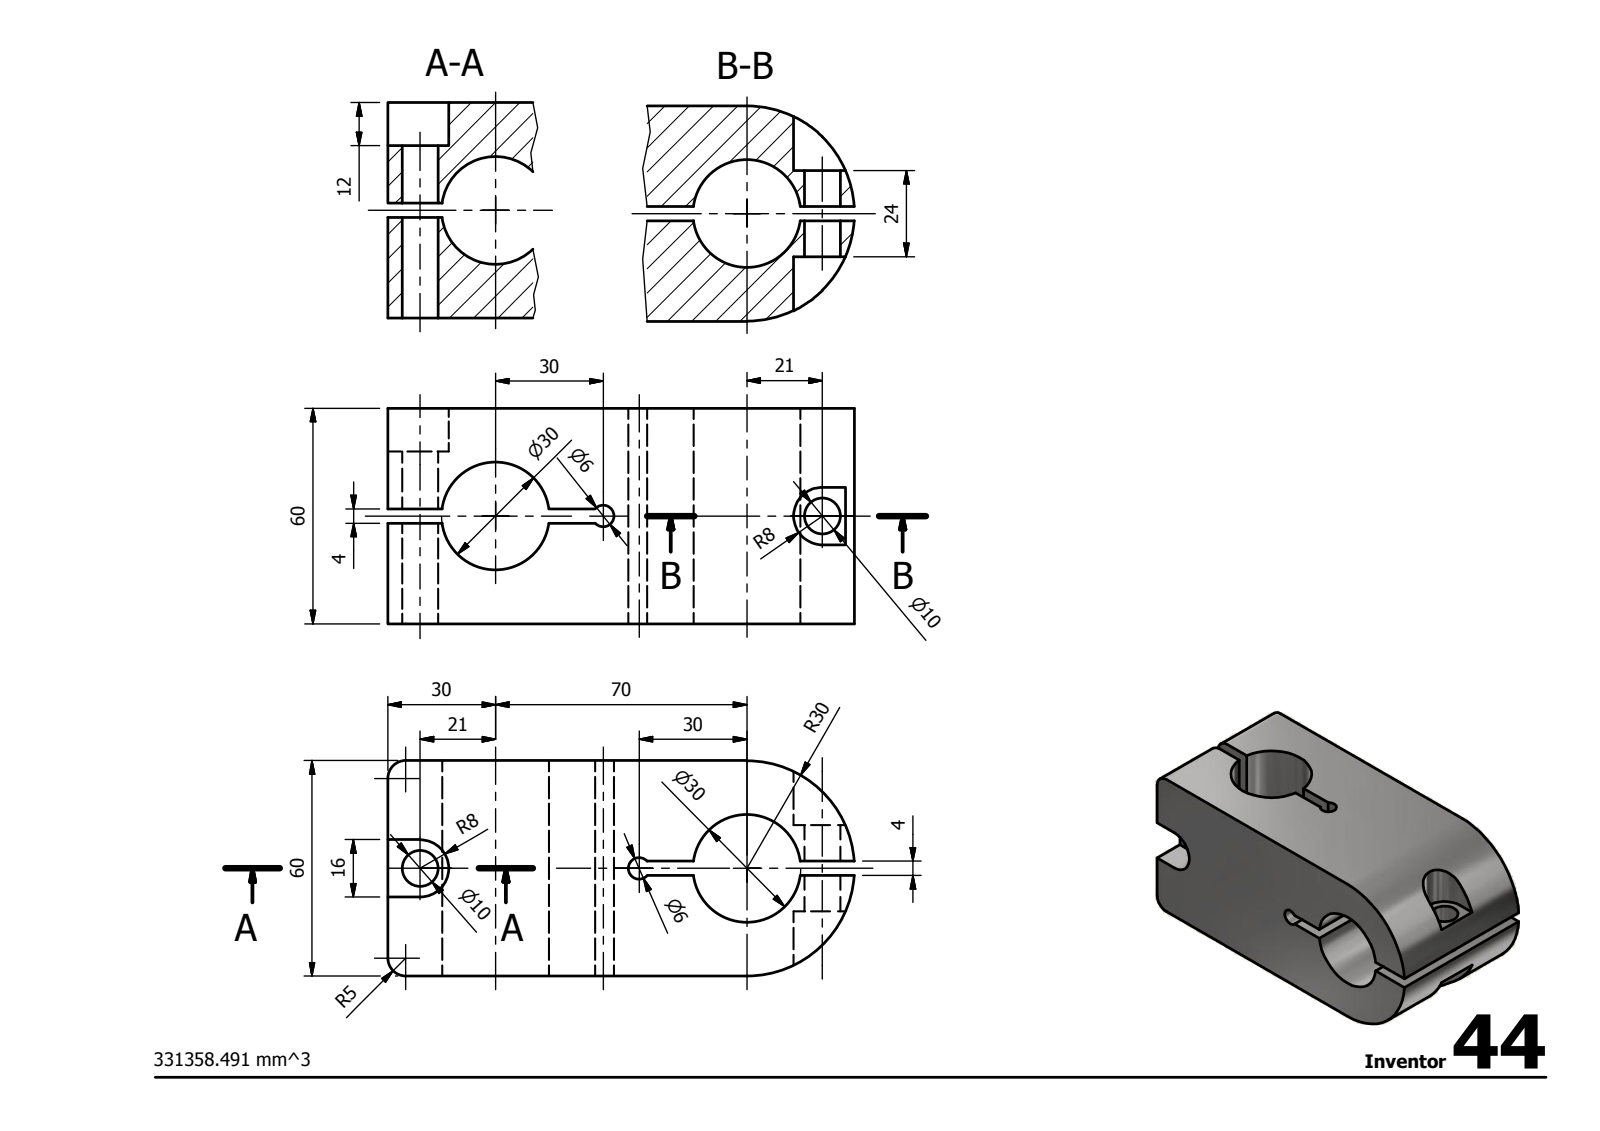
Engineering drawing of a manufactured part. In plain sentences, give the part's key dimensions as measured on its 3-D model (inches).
Its 3-D file was written by "Autodesk Inventor 2014 (AUTOMOTIVE_DESIGN)". It is 1 solid with 42 faces: 23 planar, 19 cylindrical and 0 other. Overall it measures 5.115 by 2.362 by 2.362 inches. Its volume is 20.22 cubic inches and its surface area 82.22 square inches. Round holes: 2 of diameter 0.394, 2 of diameter 1.181. Partial cylindrical surfaces (rounded edges, fillets, slot ends): 2 of radius 0.118, 2 of radius 0.197, 2 of radius 0.315, 1 of radius 1.181. The main face-to-face distances are 2.362, 1.102, 1.26, 0.157, 0.394, 0.787, 0.866, 1.496, 0.236, 0.63. The hole center spacings are 3.583.
